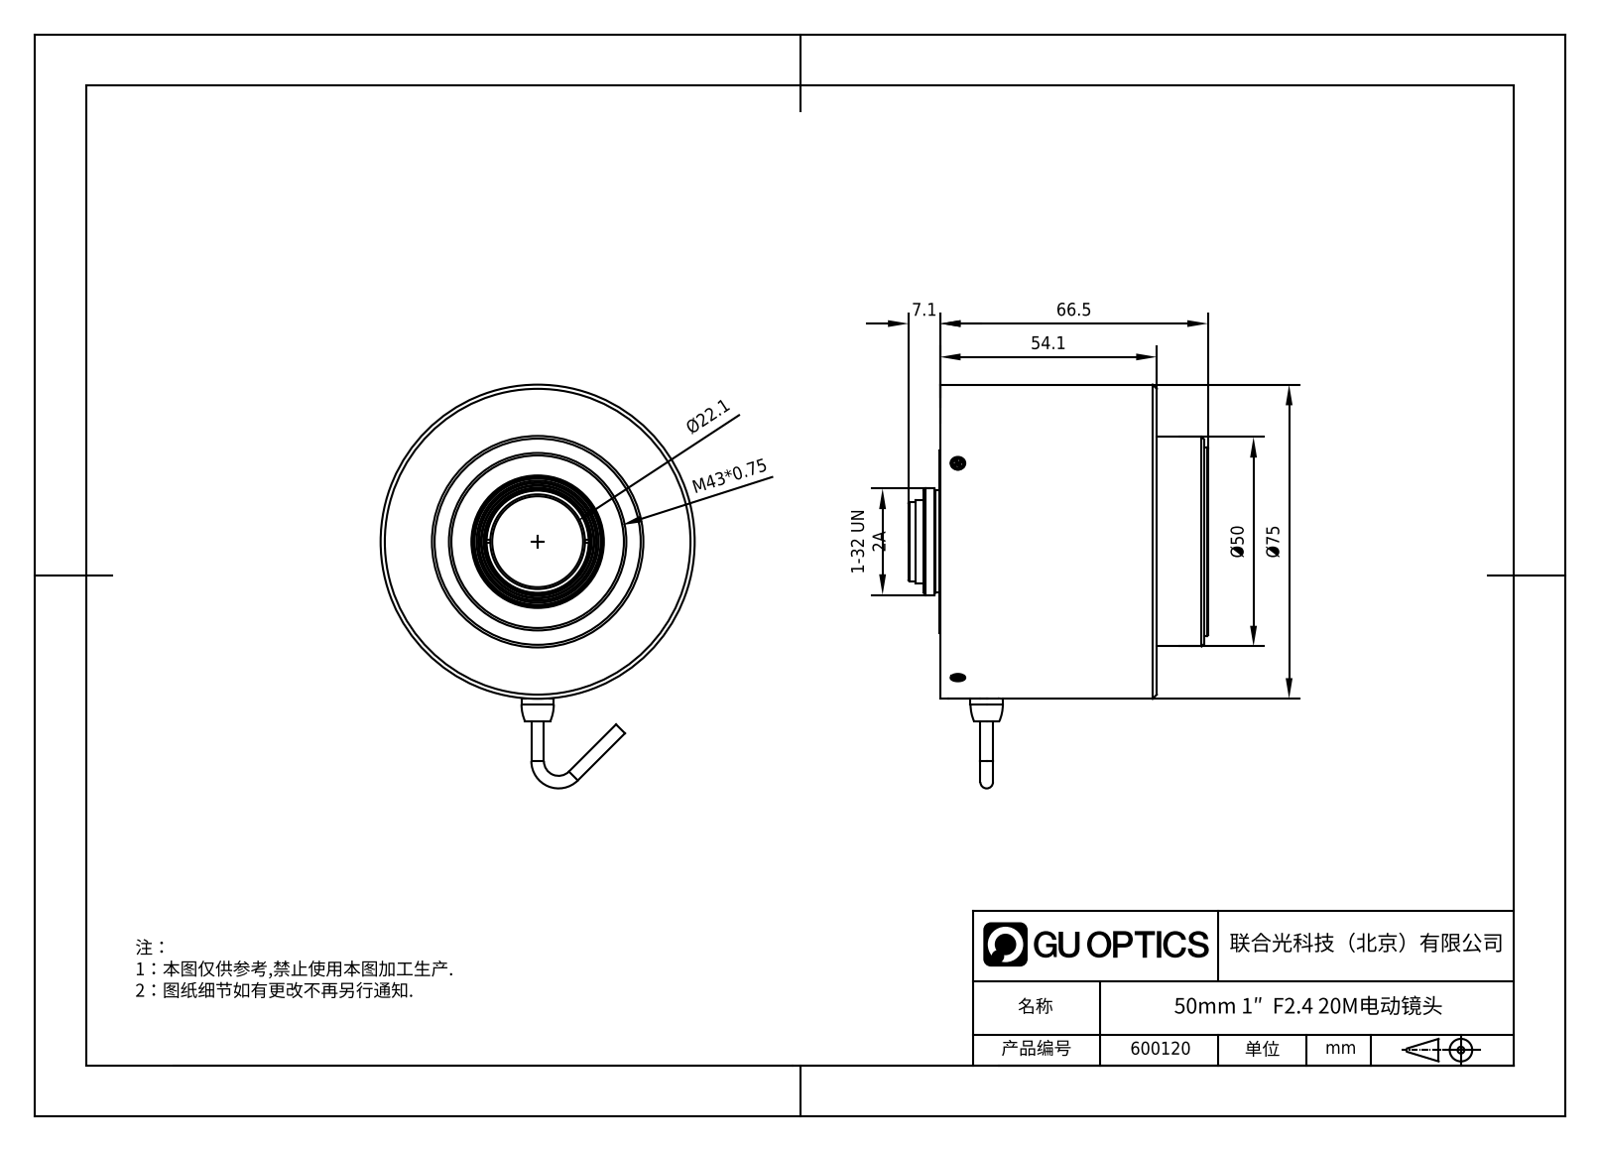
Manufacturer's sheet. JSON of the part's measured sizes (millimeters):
{"part_name": "600120", "step_written_by": "SolidWorks 2020 (CONFIG_CONTROL_DESIGN)", "units": "millimeters", "bodies": {"solids": 0, "faces": 390, "planar": 281, "cylindrical": 69, "other": 40}, "overall_size": [96.4, 75, 73.55], "round_holes": [[3, 12], [2.2, 6], [1.7, 2], [2, 1], [7.7, 1], [19.4, 1], [21, 1], [24.54, 1], [25.4, 1], [32.4, 1], [44, 1], [45, 1]], "round_bosses_or_shafts": [[2, 6], [3.5, 5], [4, 4], [1.8, 2], [43, 1], [42.5, 1], [30.5, 1], [30, 1]], "partial_cylinders_radius": [[3, 2], [13.7, 1], [36, 1]], "face_to_face_distances": [53.78, 53.88, 7.92, 61.7, 61.8, 65.3, 3.5, 11.42, 65.2, 4], "hole_center_spacings": [29, 41.01, 17.25, 29.88, 33.74, 44.78, 58, 6.87]}
